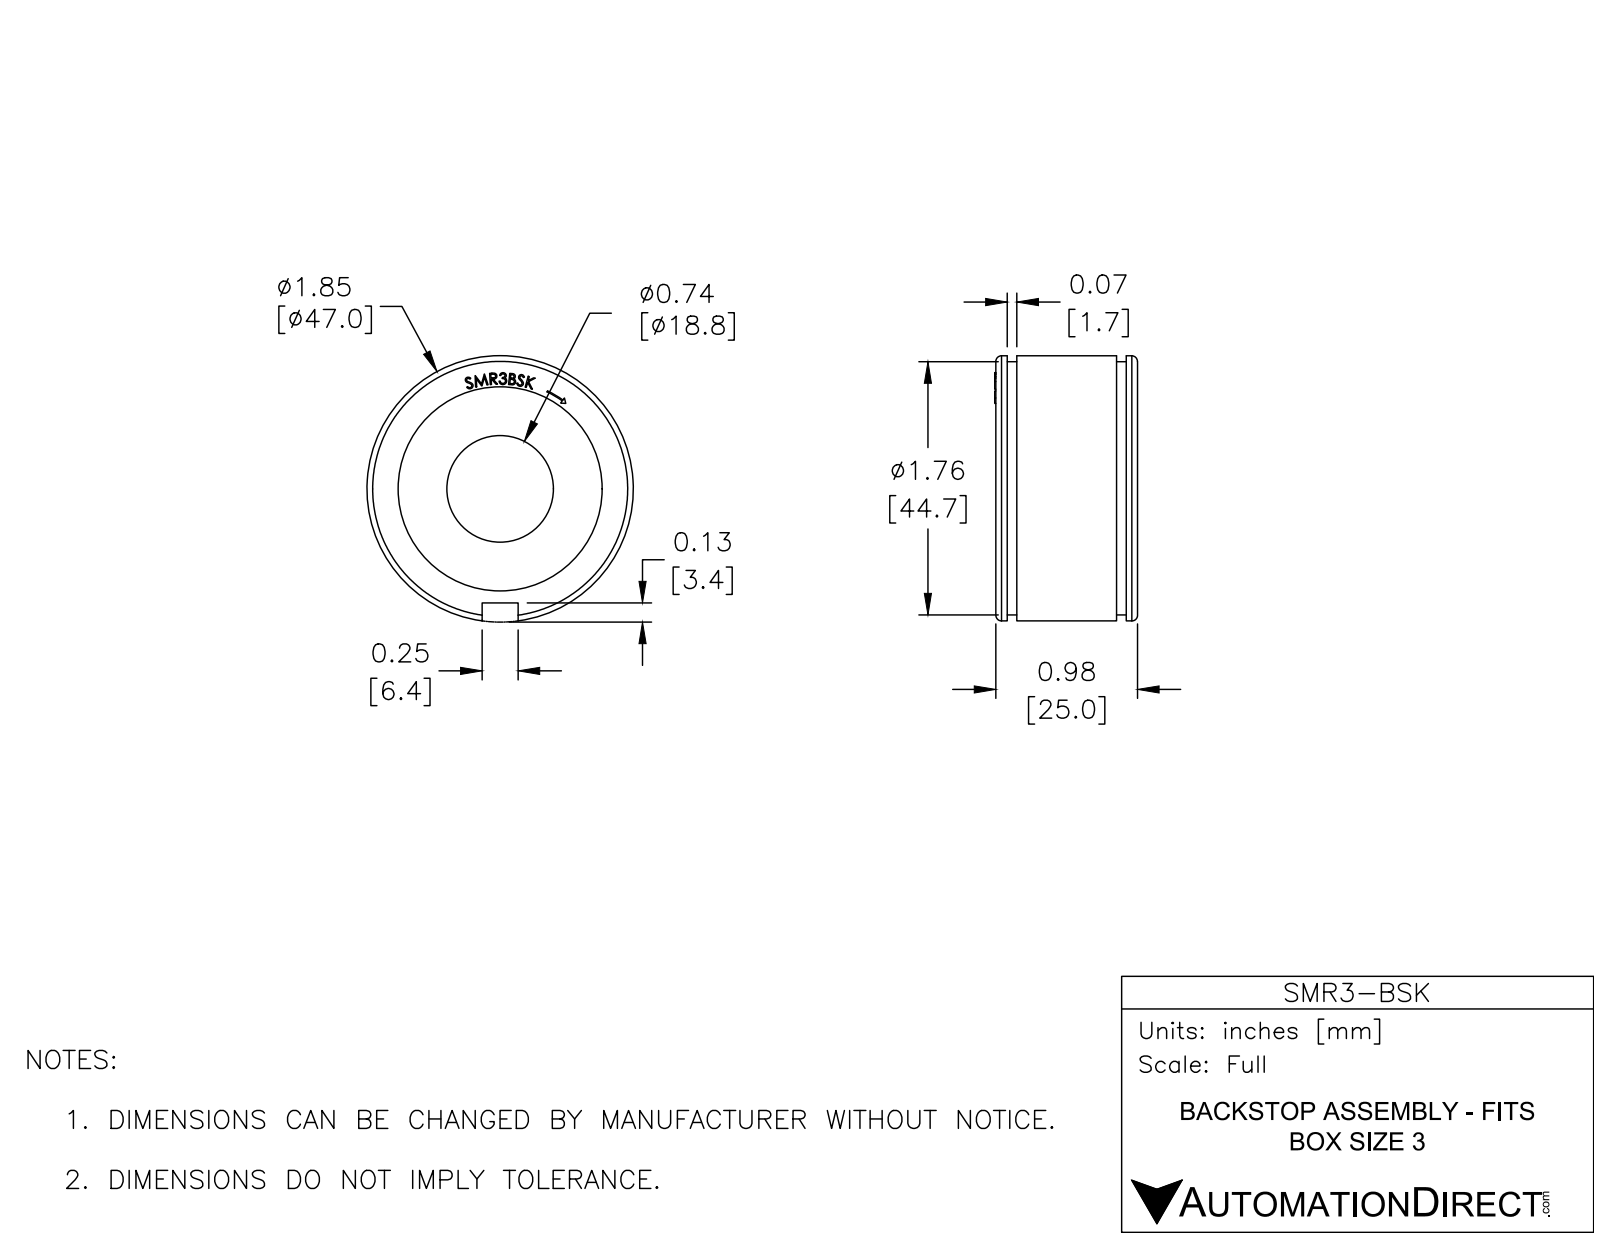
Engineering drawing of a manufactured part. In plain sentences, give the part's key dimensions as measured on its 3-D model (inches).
The part is named "SMR3-BSK". Its 3-D file was written by "SolidWorks 2016 (AUTOMOTIVE_DESIGN)". It is 1 solid with 165 faces: 78 planar, 23 cylindrical and 64 other. Overall it measures 1.85 by 1.842 by 0.992 inches. Its volume is 2.113 cubic inches and its surface area 13.48 square inches. Round holes: 1 of diameter 0.74, 1 of diameter 1.417. Round bosses or shafts: 1 of diameter 1.85, 1 of diameter 1.768. Partial cylindrical surfaces (rounded edges, fillets, slot ends): 1 of radius 0.748, 1 of radius 0.756. The main face-to-face distances are 0.02, 0.965, 0.945, 0.984, 0.146, 0.839, 0.126, 0.819, 0.079, 0.906.
